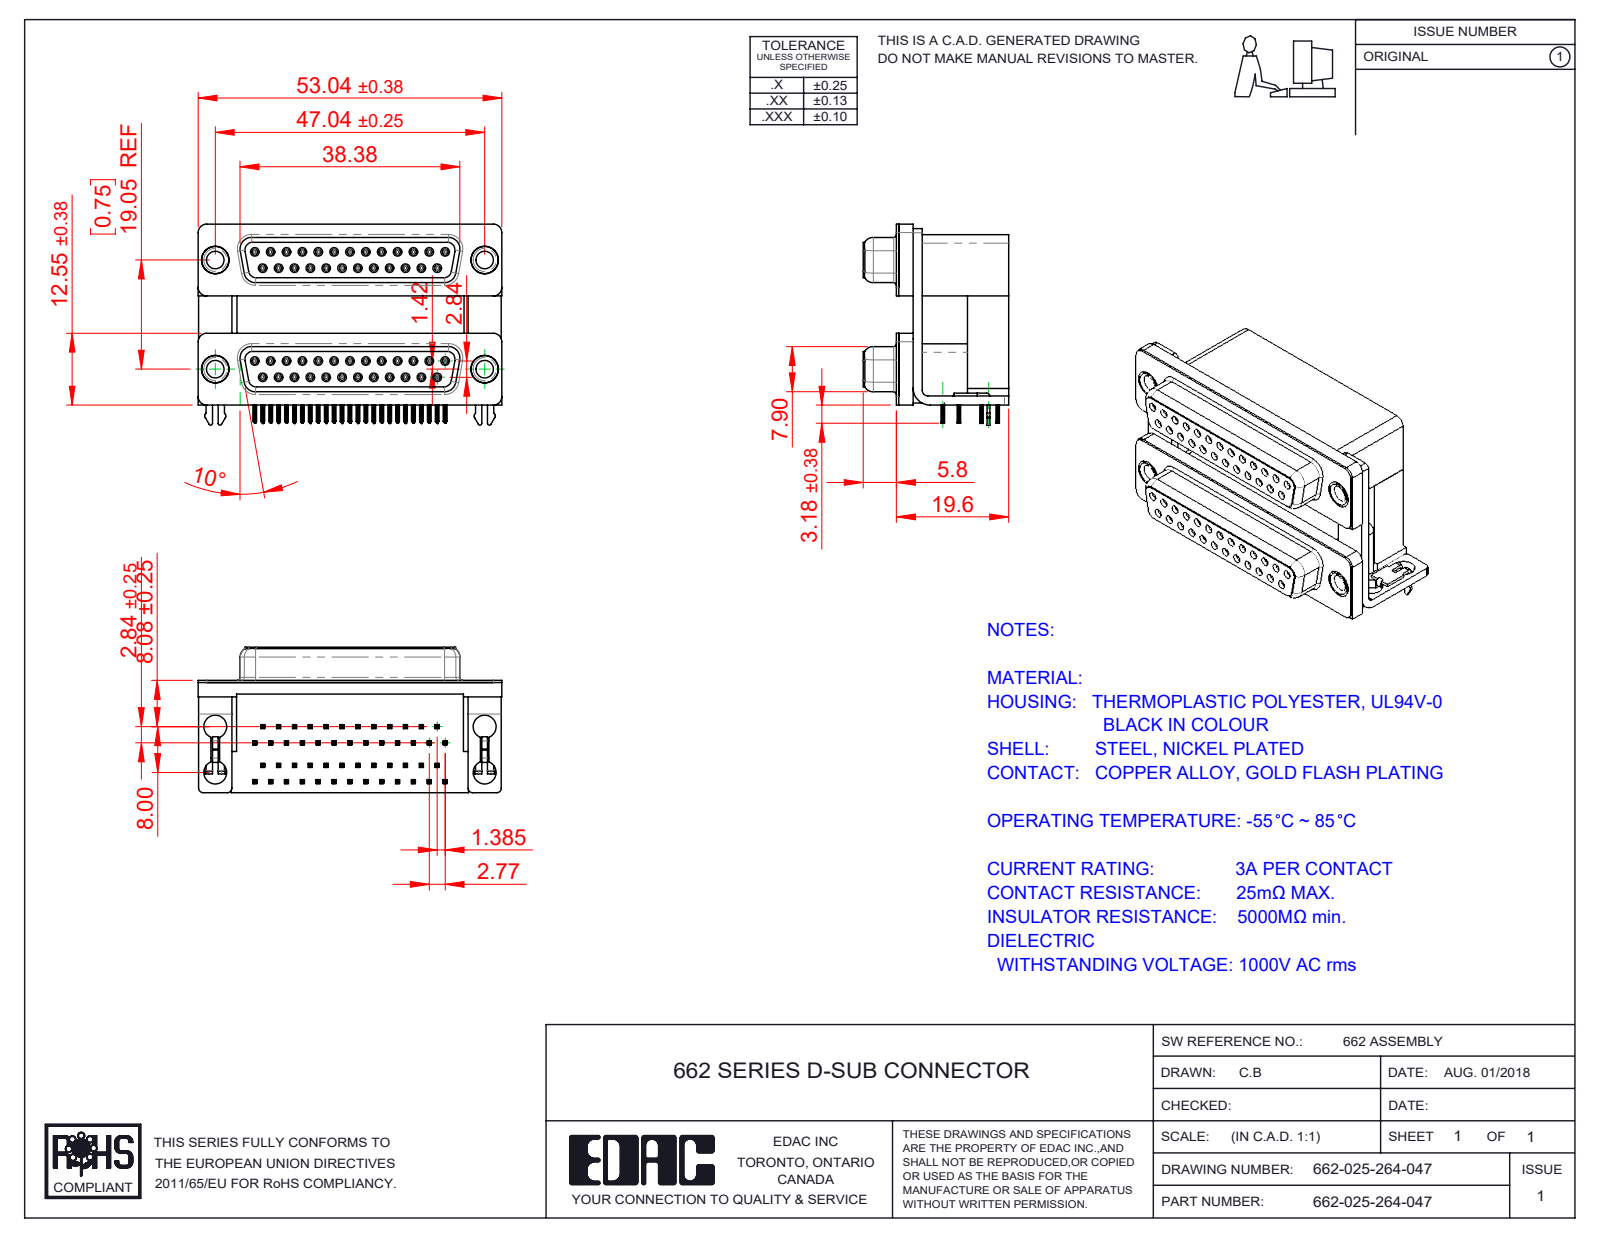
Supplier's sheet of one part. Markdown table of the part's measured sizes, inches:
| quantity | value |
| --- | --- |
| part name | 662 Housing Lower_25 Contacts; 662-025-264-047; 662 Contact Bottom Upper_M; 662 Contact Top Lower (+8 more) |
| STEP written by | SolidWorks 2020 (CONFIG_CONTROL_DESIGN) |
| units | inches |
| bodies | 63 solids, 7816 faces (3654 planar, 1798 cylindrical, 2364 other) |
| overall size | 2.088 × 1.382 × 1 |
| volume | 1.453 in³ |
| surface area | 40.24 in² |
| round holes (diameter × count) | 0.031 × 50, 0.035 × 50, 0.157 × 8, 0.12 × 4, 0.138 × 4, 0.189 × 4, 0.197 × 4 |
| round bosses / shafts (diameter × count) | 0.047 × 50, 0.193 × 4, 0.187 × 4, 0.152 × 4 |
| partial cylindrical surfaces (radius × count) | 0.004 × 401, 0.006 × 200, 0.014 × 100, 0.013 × 50, 0.011 × 24, 0.053 × 16, 0.059 × 14, 0.02 × 12 |
| main face-to-face distances | 0.756, 0.75, 0.472, 0.016, 0.283, 0.244, 0.421, 0.098, 0.488, 0.657 |
| hole center spacings | 0.124, 0.109, 0.218, 0.436, 0.327, 0.198, 0.545, 0.294 |
